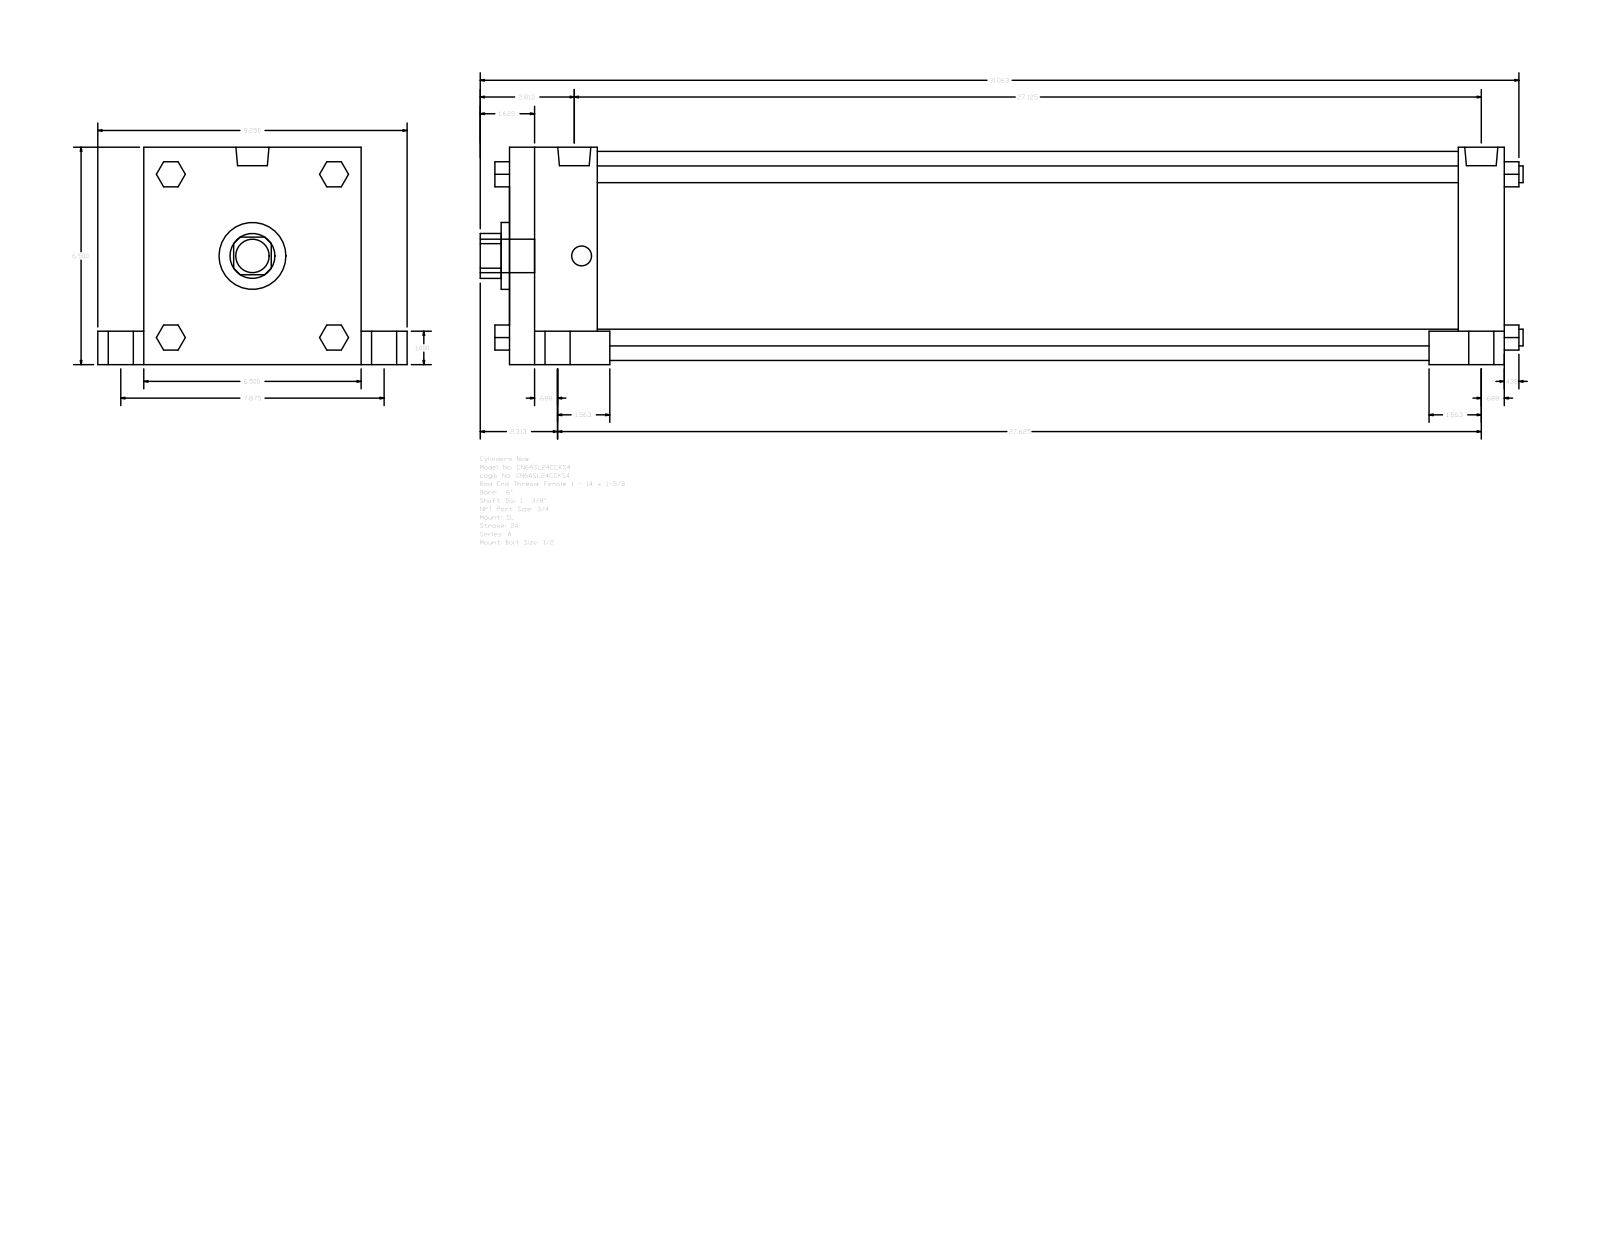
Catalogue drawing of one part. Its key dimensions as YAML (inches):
part_name: "A_SL__0600_1.375"
step_written_by: "GSSL Pune (CONFIG_CONTROL_DESIGN)"
units: inches
bodies: {solids: 0, faces: 150, planar: 114, cylindrical: 36, other: 0}
overall_size: [31.187, 9.25, 6.5]
round_holes:
  - {diameter: 1.375, count: 1}
  - {diameter: 2, count: 1}
  - {diameter: 6.25, count: 1}
round_bosses_or_shafts:
  - {diameter: 1, count: 5}
  - {diameter: 0.75, count: 4}
  - {diameter: 0.594, count: 4}
  - {diameter: 0.5, count: 4}
  - {diameter: 0.989, count: 2}
partial_cylinders:
  - {radius: 0.672, count: 1}
face_to_face_distances: [6.5, 29.75, 2.625, 27.125, 28.375, 25.75, 1.375, 1, 5.5, 1.375]
